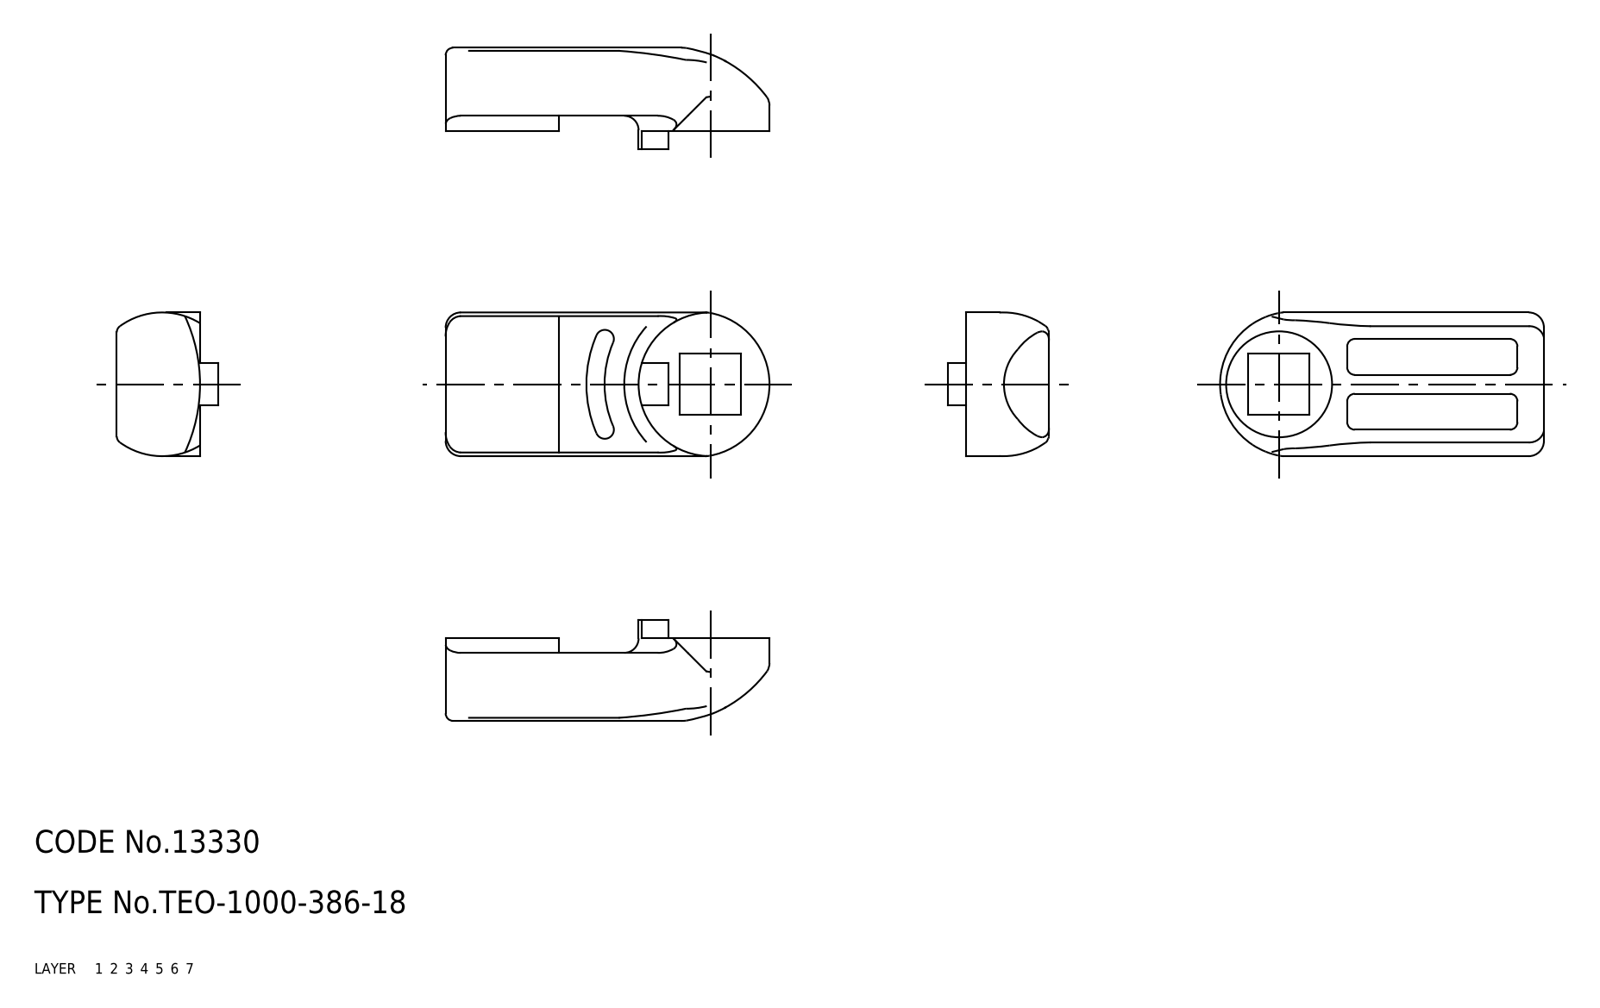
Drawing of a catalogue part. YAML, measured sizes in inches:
part_name: "cam"
step_written_by: "CADfix (AUTOMOTIVE_DESIGN)"
units: inches
bodies: {solids: 1, faces: 95, planar: 0, cylindrical: 0, other: 95}
overall_size: [1.685, 0.748, 0.528]
volume: 0.304
surface_area: 5.002
